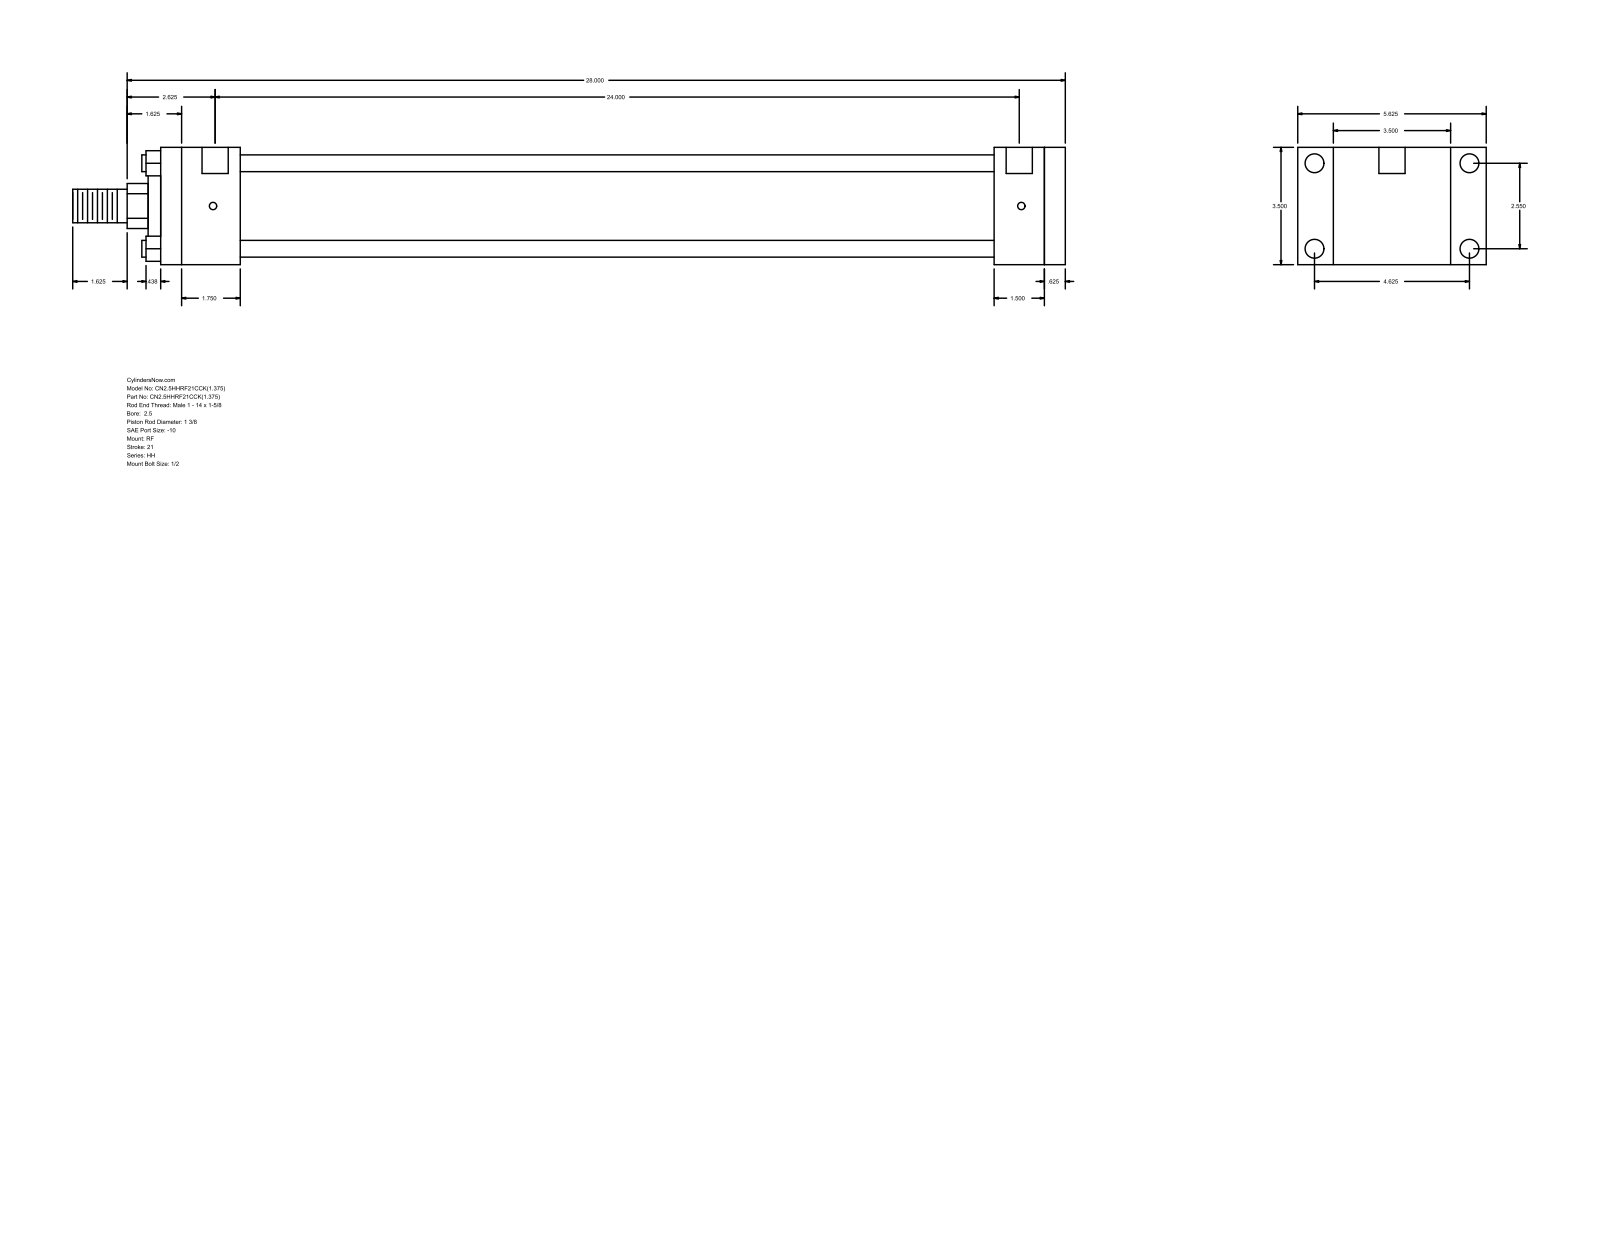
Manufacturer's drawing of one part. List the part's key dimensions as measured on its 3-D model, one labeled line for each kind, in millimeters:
Part name (STEP PRODUCT): HH_RF__0250_1.375
STEP written by: GSSL Pune (CONFIG_CONTROL_DESIGN)
Units: millimetres
Bodies: 0 solids, 92 faces (64 planar, 28 cylindrical, 0 other)
Overall size (bounding box): 752.48 × 142.88 × 88.9
Round holes (diameter × count): ⌀5.56 ×4, ⌀14.3 ×4, ⌀19.84 ×2
Round bosses / shafts (diameter × count): ⌀12.7 ×4, ⌀73.03 ×1, ⌀50.8 ×1, ⌀34.92 ×1, ⌀25.4 ×1
Partial cylindrical surfaces — rounded edges, fillets, slot ends (radius × count): R17.06 ×1
Main face-to-face distances: 88.9, 685.8, 669.93, 15.87, 53.97, 60.32, 609.61, 625.48, 631.83, 571.51
Hole centre spacings: 64.76, 117.48, 134.15, 612.77, 1.58, 1.59, 609.6, 611.18
